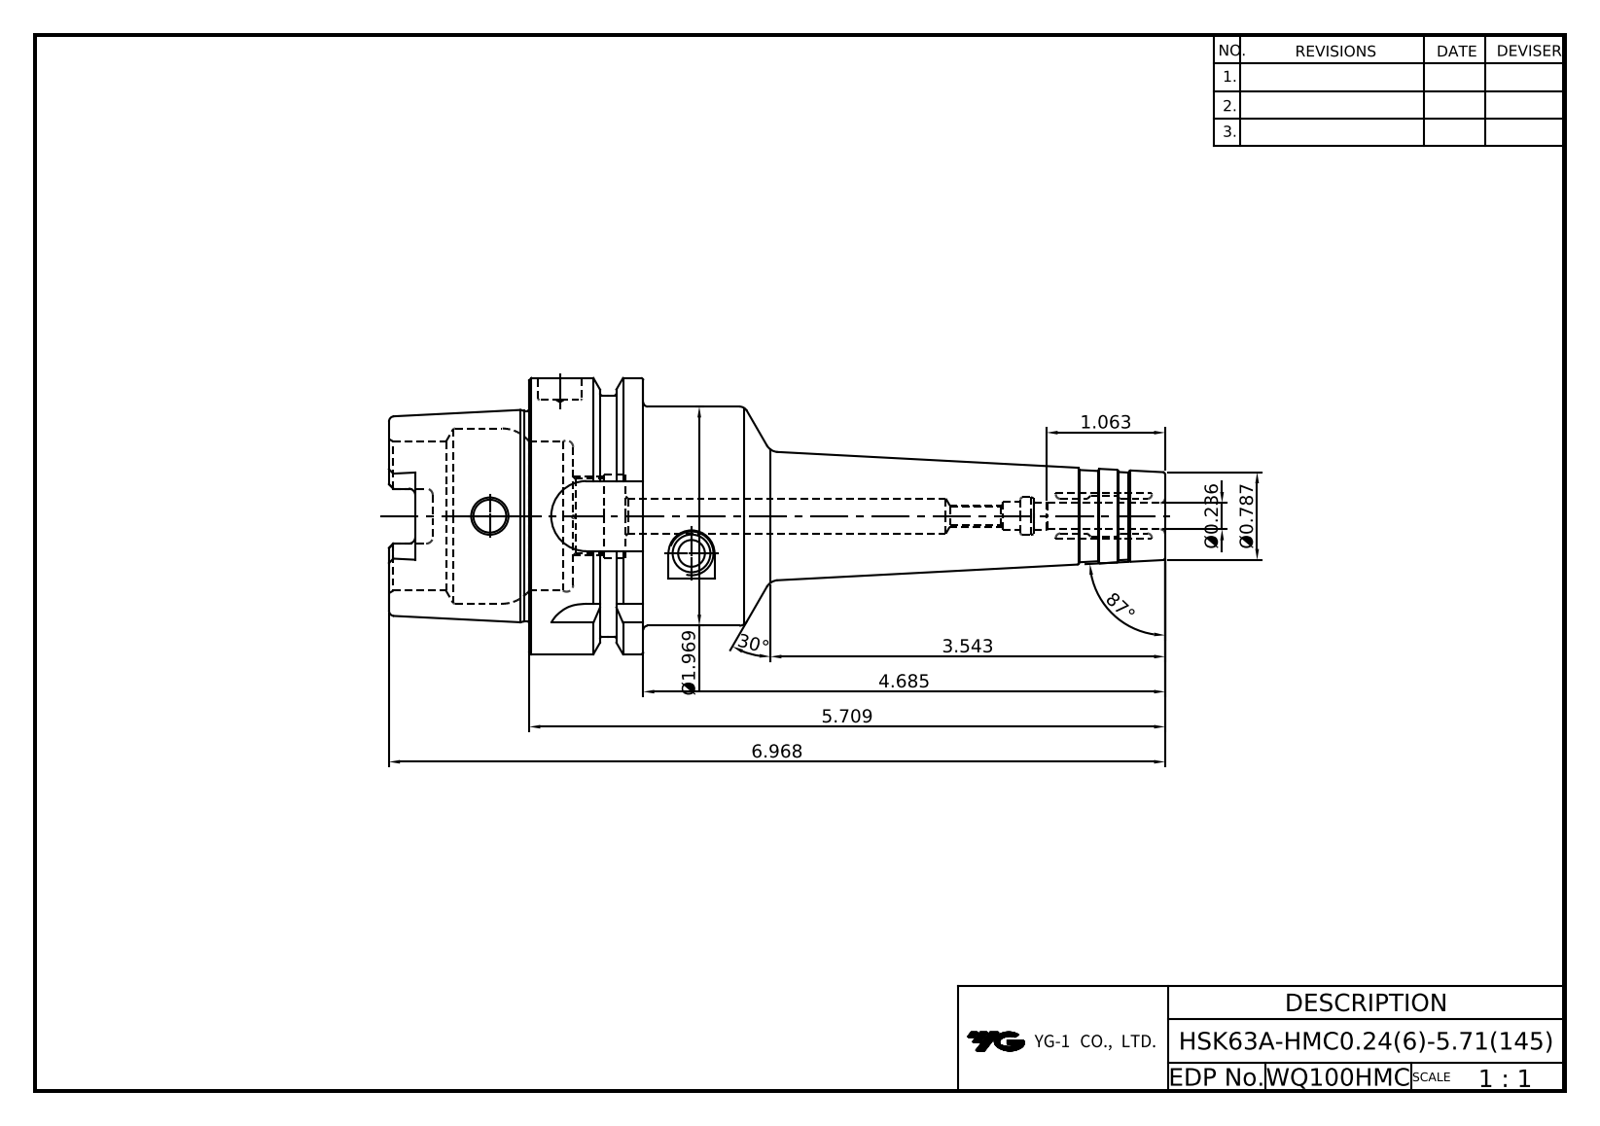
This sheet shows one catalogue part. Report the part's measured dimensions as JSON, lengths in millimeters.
{"part_name": "LO-HSK63A-HMC6-145", "step_written_by": "Autodesk Inventor 2020 (AUTOMOTIVE_DESIGN)", "units": "millimeters", "bodies": {"solids": 1, "faces": 136, "planar": 42, "cylindrical": 34, "other": 60}, "overall_size": [177, 63, 63], "volume_mm3": 173016, "surface_area_mm2": 35336, "round_holes": [[4.92, 1], [6, 1], [6.6, 1], [7.5, 1], [8, 1], [10, 1], [16.92, 1], [19, 1], [34, 1], [40, 1]], "round_bosses_or_shafts": [[63, 1], [55, 1], [50, 1], [48.04, 1]], "partial_cylinders_radius": [[1.5, 6], [2.88, 4], [8, 4]], "face_to_face_distances": [26, 10, 16, 32, 42, 58, 53, 4, 22, 12]}
